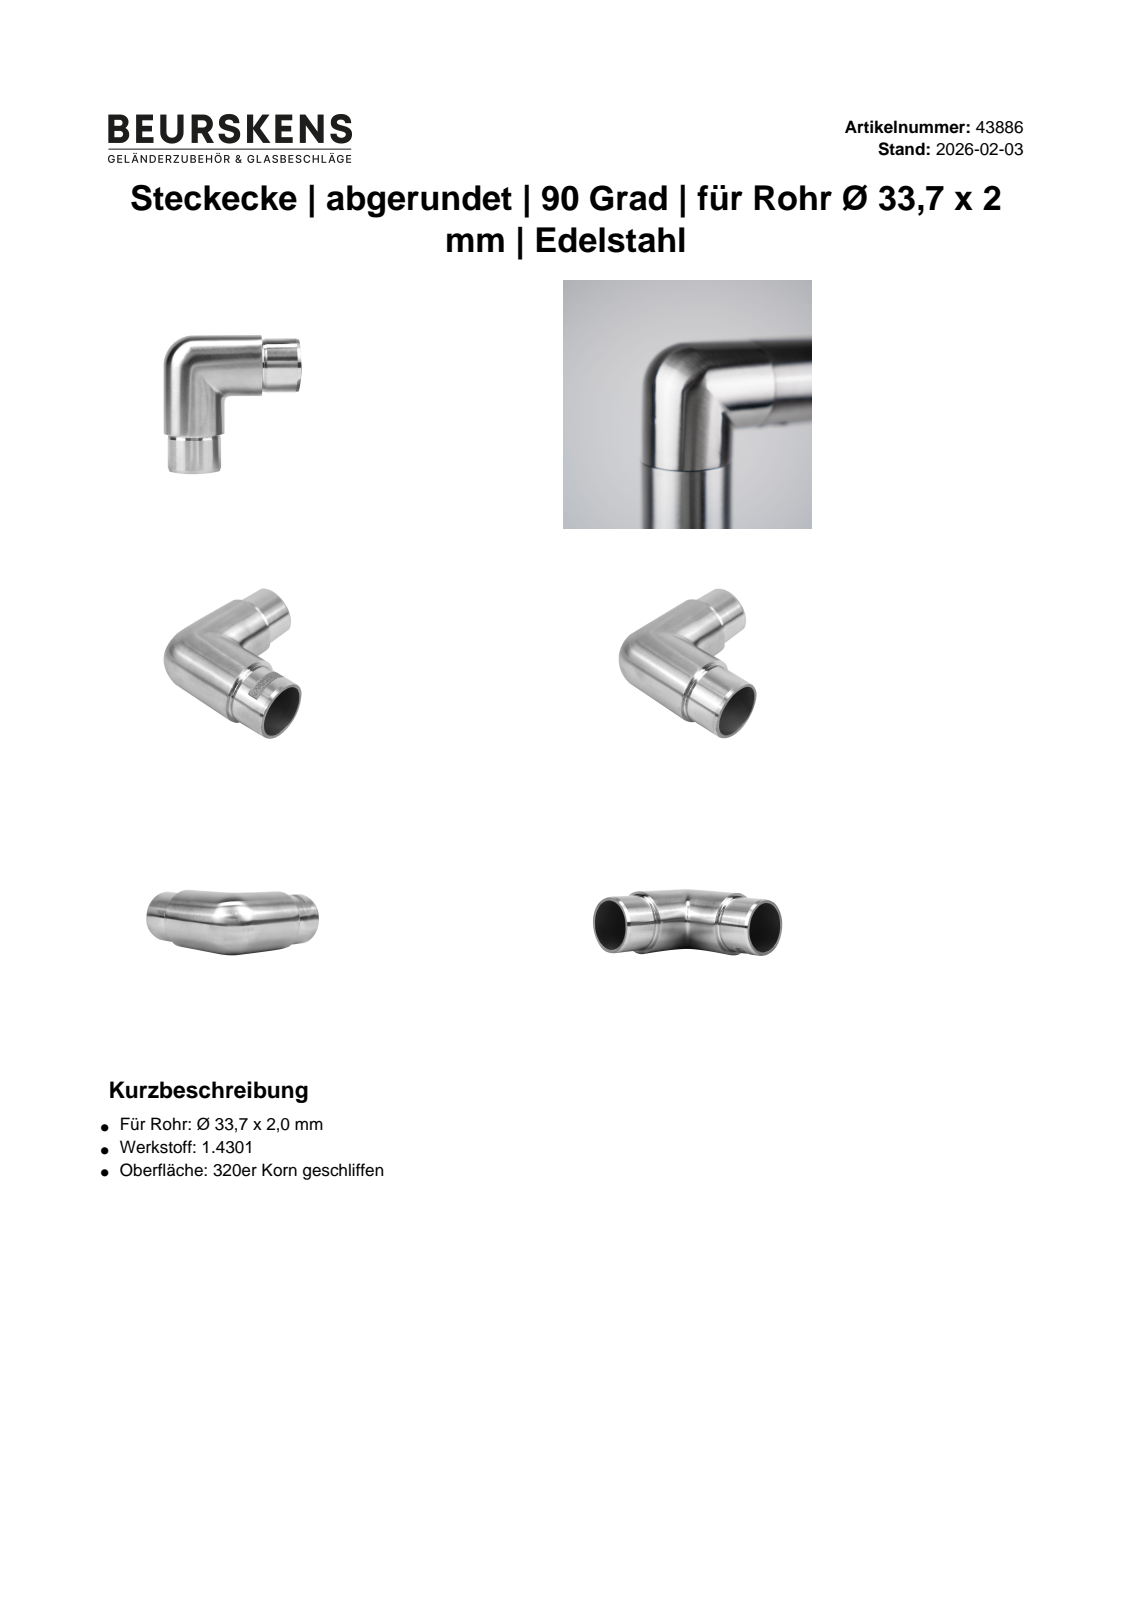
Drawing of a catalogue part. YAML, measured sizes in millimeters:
part_name: "43886"
step_written_by: "Autodesk Inventor 2022 (AUTOMOTIVE_DESIGN)"
units: millimeters
bodies: {solids: 1, faces: 16, planar: 6, cylindrical: 8, other: 2}
overall_size: [74, 74, 33.7]
volume: 22028
surface_area: 22375
round_holes:
  - {diameter: 25.7, count: 2}
  - {diameter: 29.7, count: 2}
round_bosses_or_shafts:
  - {diameter: 33.7, count: 2}
face_to_face_distances: [20, 22, 2]
